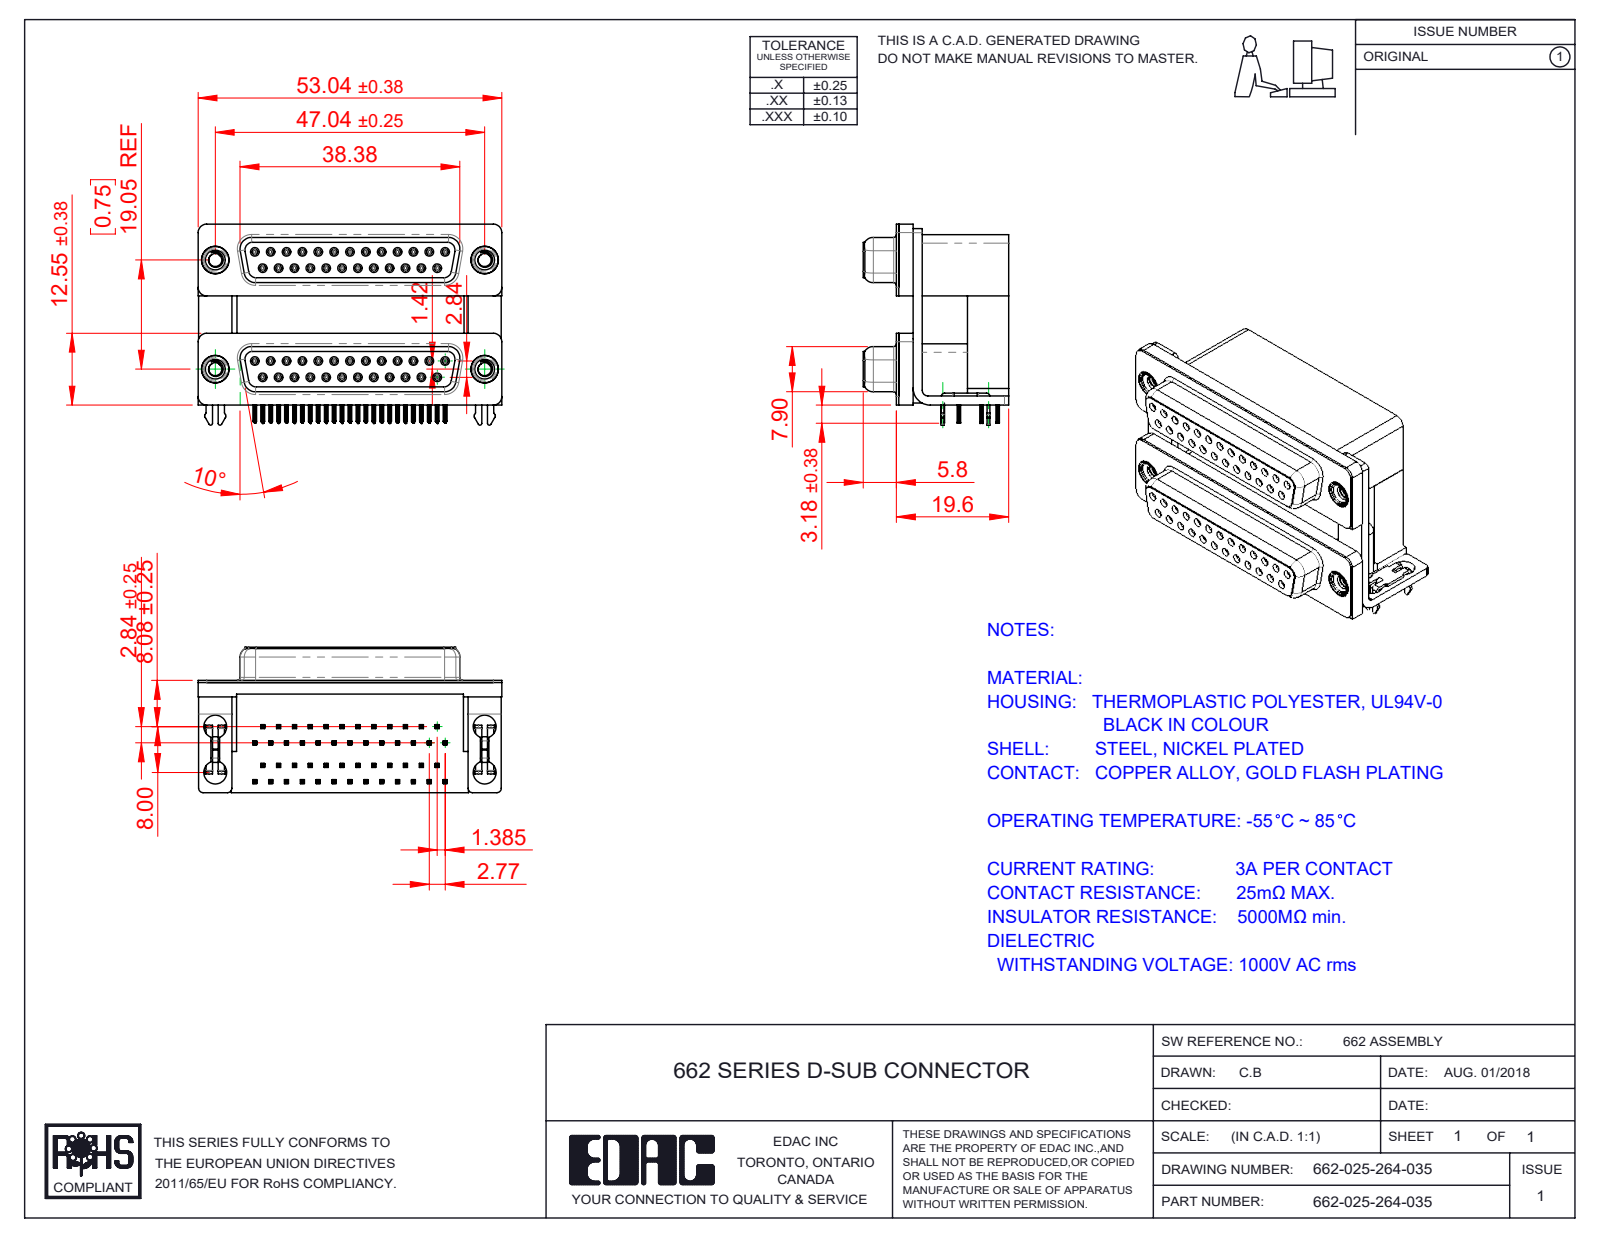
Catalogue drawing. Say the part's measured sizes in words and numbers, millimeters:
The part is named "662-025-264-035; 662 Housing Spacer_25 Contacts M; 662 Contact Top Upper_M; 662 Contact Bottom Upper_M (+8 more)". Its 3-D file was written by "SolidWorks 2020 (CONFIG_CONTROL_DESIGN)". It is 63 solids with 7944 faces: 3678 planar, 1854 cylindrical and 2412 other. Overall it measures 53.04 by 35.1 by 25.4 millimeters. Its volume is 23 855 cubic millimeters and its surface area 26 100 square millimeters. Round holes: 50 of diameter 0.8, 50 of diameter 0.9, 8 of diameter 4, 4 of diameter 2.26, 4 of diameter 3.5, 4 of diameter 4.8, 4 of diameter 5. Round bosses or shafts: 50 of diameter 1.2, 4 of diameter 4.9, 4 of diameter 4.75, 4 of diameter 3.9. Partial cylindrical surfaces (rounded edges, fillets, slot ends): 402 of radius 0.1, 200 of radius 0.15, 100 of radius 0.35, 50 of radius 0.34, 24 of radius 0.28, 16 of radius 1.35, 14 of radius 1.5, 12 of radius 0.5. The main face-to-face distances are 19.2, 19.05, 12, 0.4, 7.2, 6.2, 10.69, 2.5, 16.7, 9.5. The hole center spacings are 3.16, 2.77, 5.54, 11.08, 8.31, 5.03, 13.85, 7.48.
